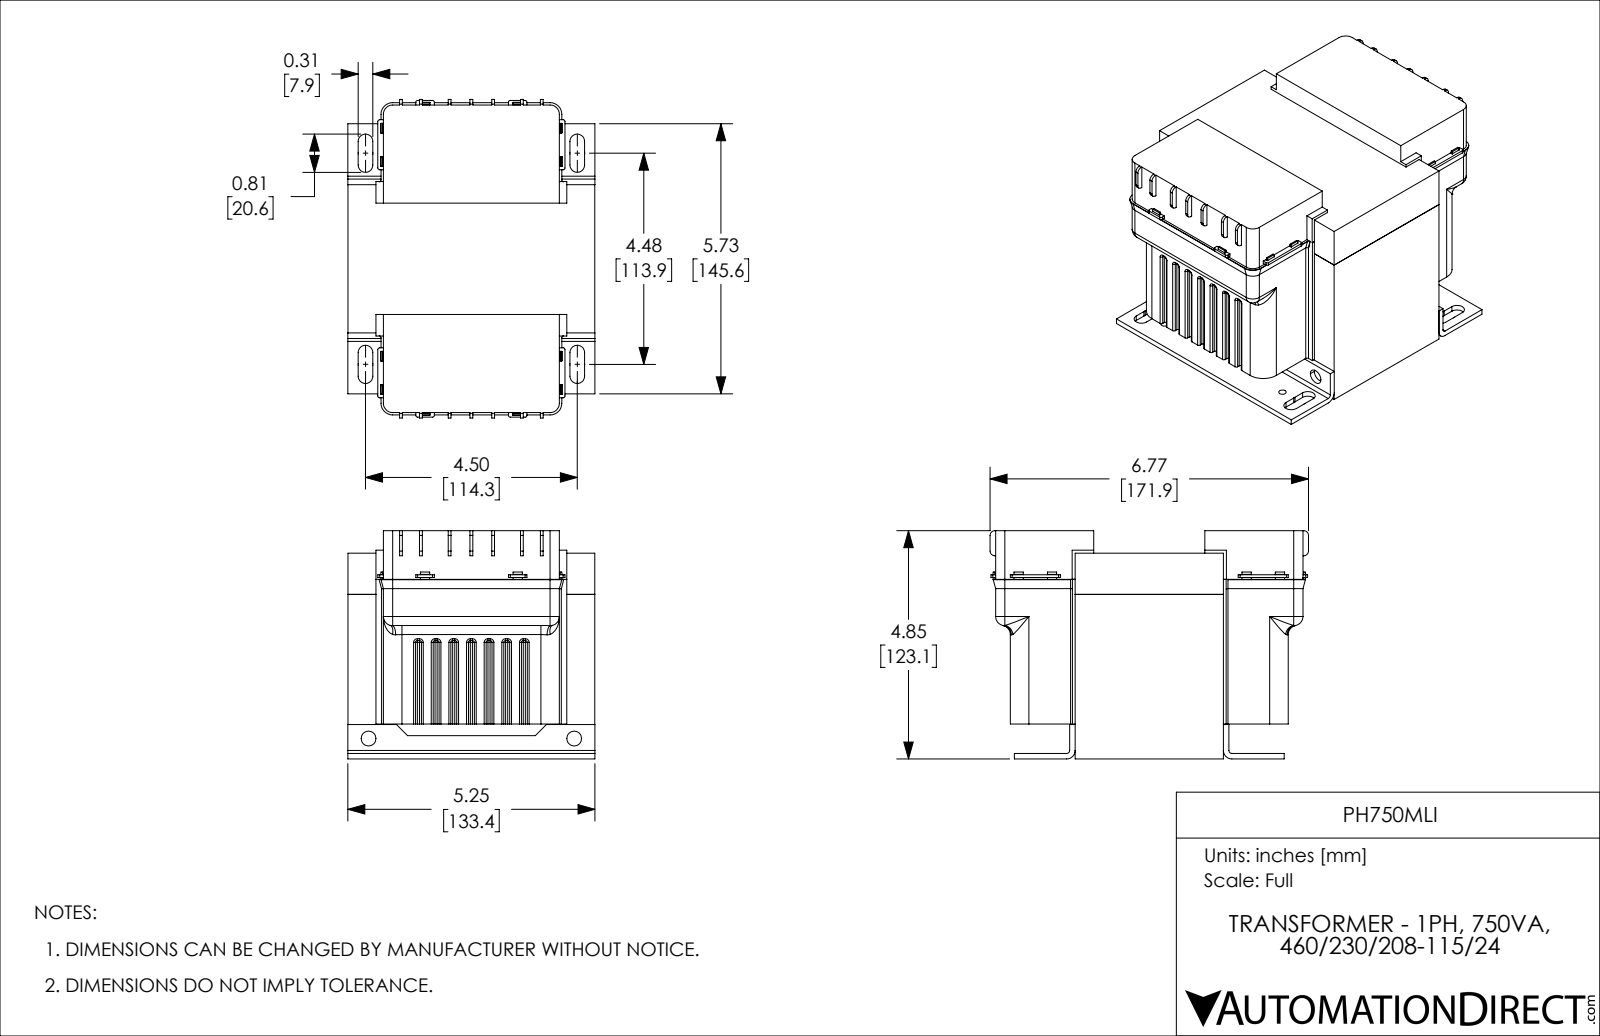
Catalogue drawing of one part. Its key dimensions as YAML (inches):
part_name: "PH750MLI"
step_written_by: "SolidWorks 2018 (AUTOMOTIVE_DESIGN)"
units: inches
bodies: {solids: 8, faces: 722, planar: 414, cylindrical: 214, other: 94}
overall_size: [6.767, 5.25, 4.847]
volume: 122.2
surface_area: 332.6
round_holes:
  - {diameter: 0.157, count: 4}
partial_cylinders:
  - {radius: 0.039, count: 94}
  - {radius: 0.197, count: 10}
  - {radius: 0.156, count: 8}
  - {radius: 0.1, count: 4}
  - {radius: 0.157, count: 4}
  - {radius: 0.248, count: 4}
  - {radius: 0.394, count: 4}
  - {radius: 0.062, count: 2}
face_to_face_distances: [3.15, 3.496, 3.814, 0.318, 4.37, 0.874, 0.556, 0.752, 4.492, 4.847]
hole_center_spacings: [3.543, 4.553, 5.769]
